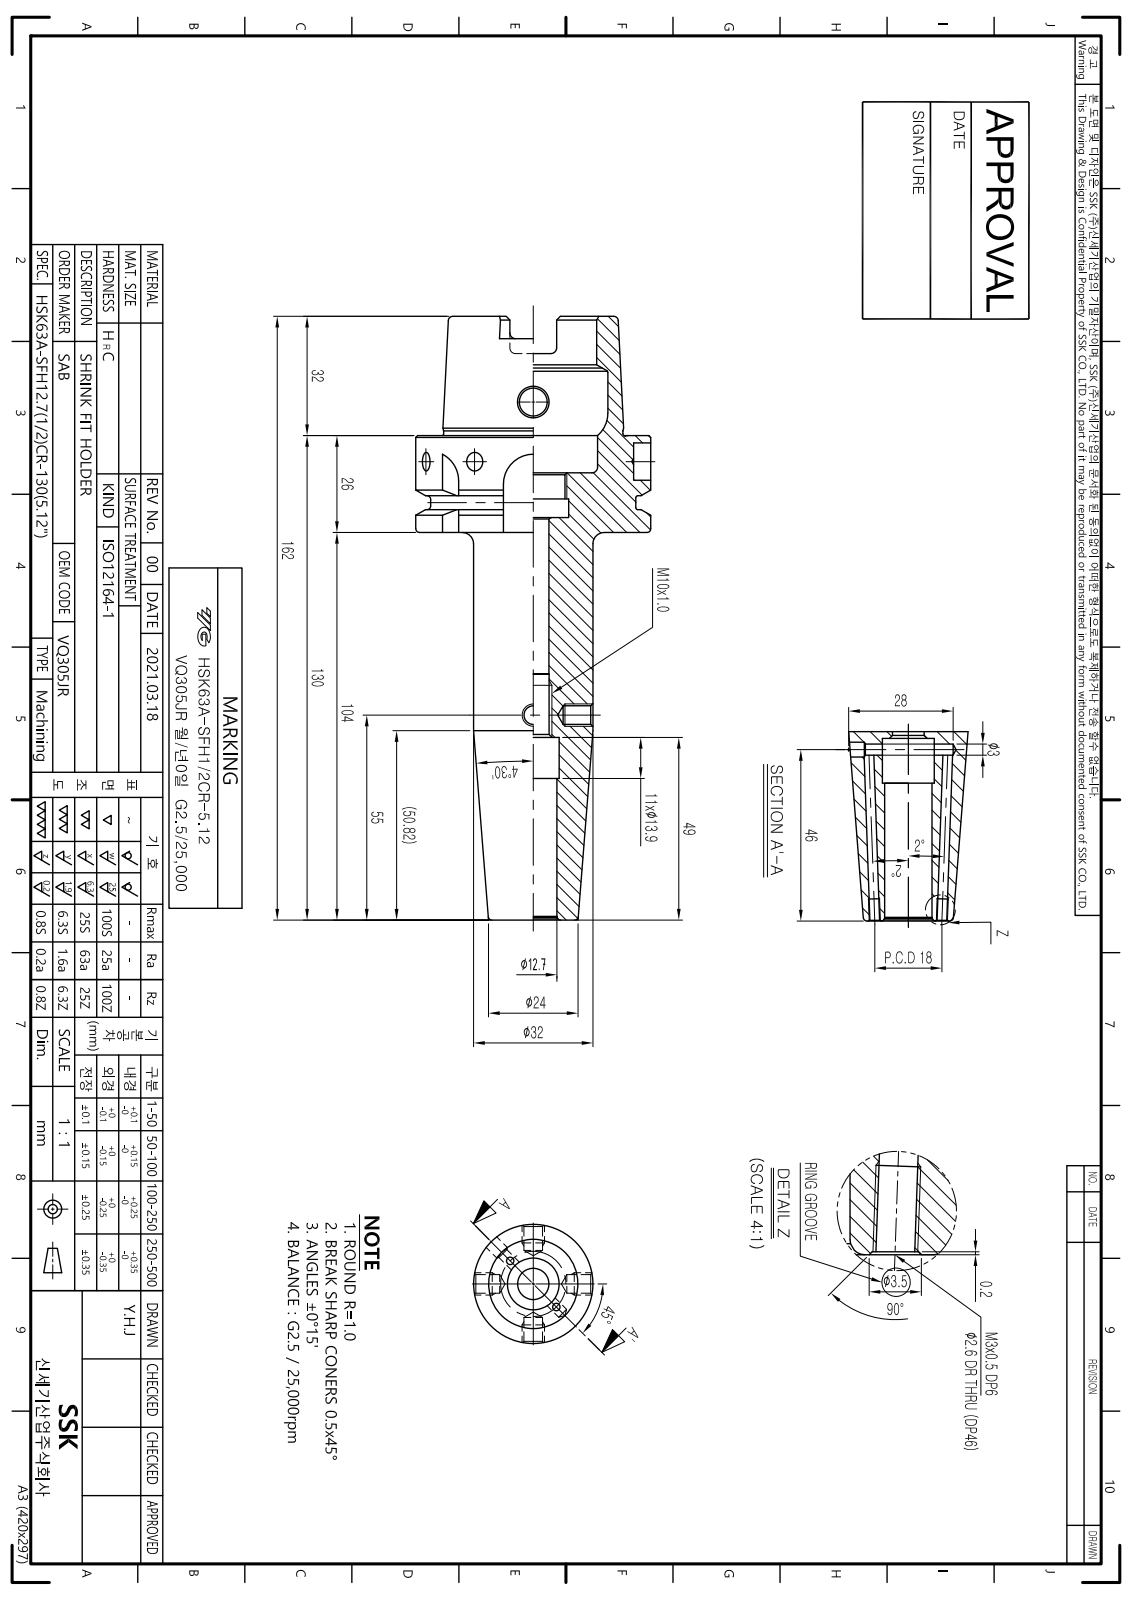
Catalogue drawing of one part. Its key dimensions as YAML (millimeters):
part_name: "LO-HSK63A-SFH12.7CR-130"
step_written_by: "Autodesk Inventor 2022 (AUTOMOTIVE_DESIGN)"
units: millimeters
bodies: {solids: 1, faces: 121, planar: 42, cylindrical: 36, other: 43}
overall_size: [162, 63, 63]
volume: 145781
surface_area: 35827
round_holes:
  - {diameter: 2.46, count: 2}
  - {diameter: 7.5, count: 1}
  - {diameter: 8.4, count: 1}
  - {diameter: 8.92, count: 1}
  - {diameter: 10, count: 1}
  - {diameter: 12.7, count: 1}
  - {diameter: 13.9, count: 1}
  - {diameter: 16.92, count: 1}
  - {diameter: 19, count: 1}
  - {diameter: 34, count: 1}
  - {diameter: 40, count: 1}
round_bosses_or_shafts:
  - {diameter: 63, count: 1}
  - {diameter: 55, count: 1}
  - {diameter: 48.04, count: 1}
  - {diameter: 32, count: 1}
partial_cylinders:
  - {radius: 1.5, count: 6}
  - {radius: 2.88, count: 4}
  - {radius: 8, count: 4}
face_to_face_distances: [26, 10, 16, 32, 42, 58, 53, 22, 4, 12]
